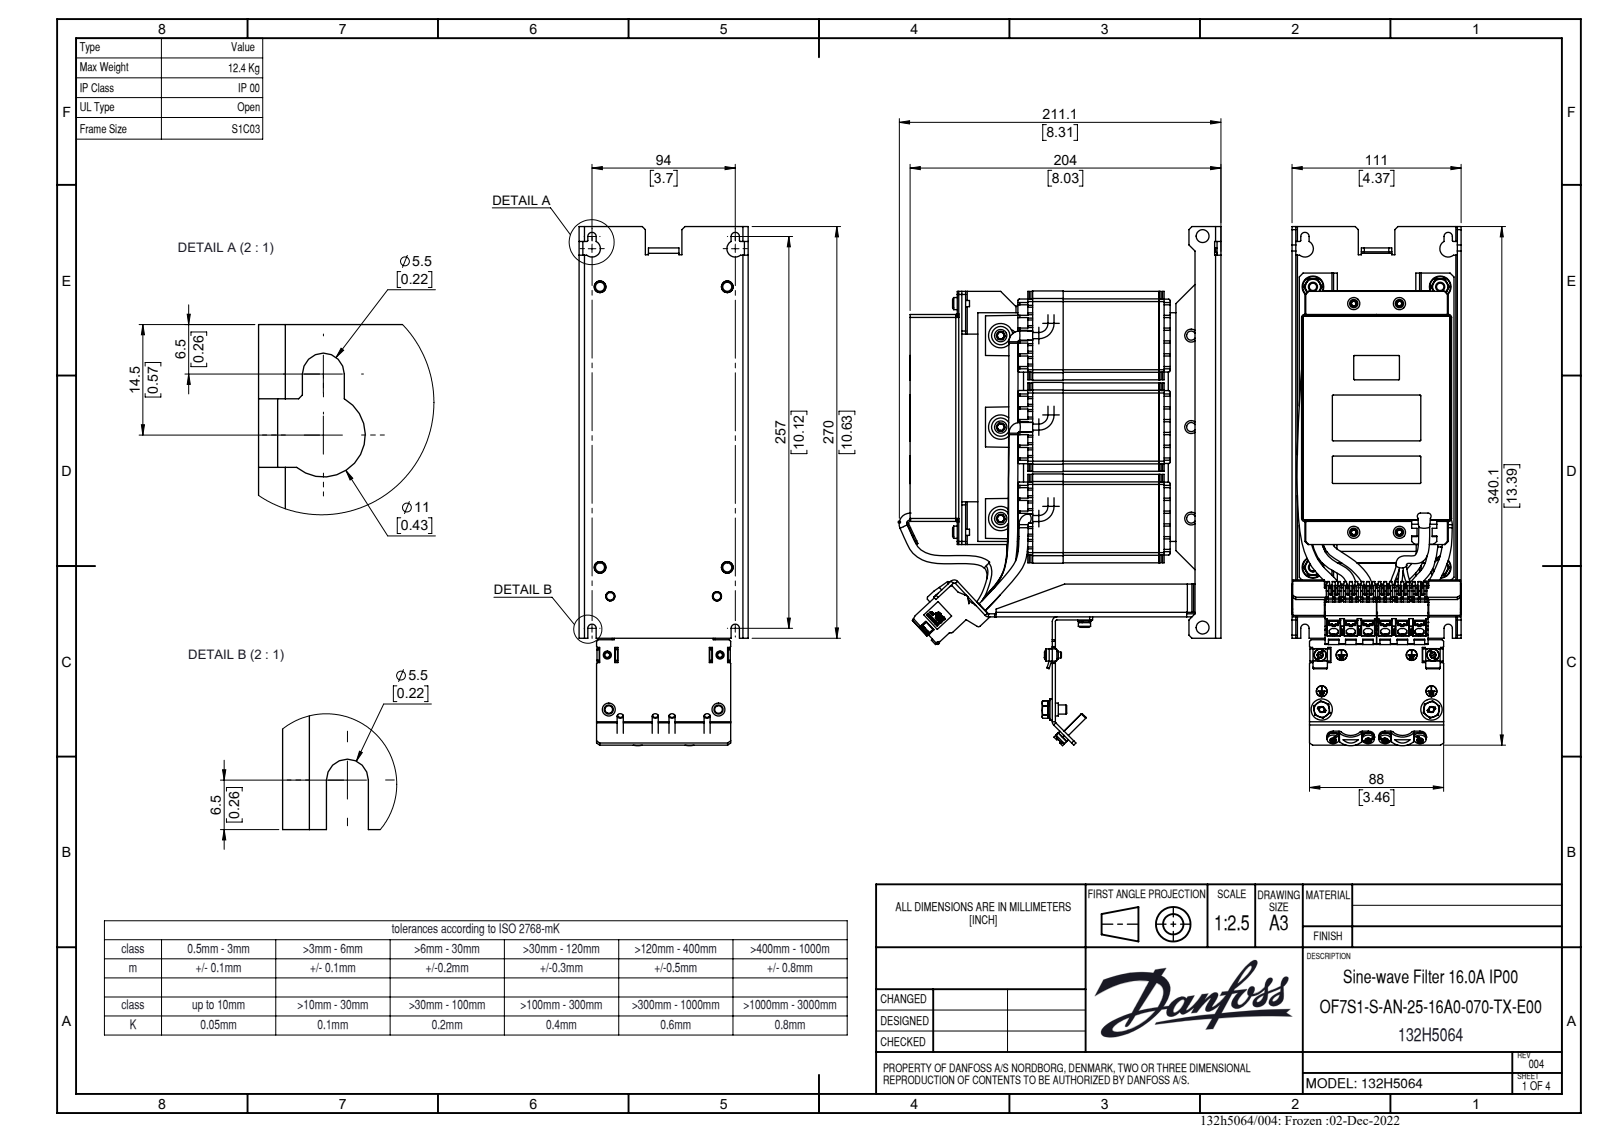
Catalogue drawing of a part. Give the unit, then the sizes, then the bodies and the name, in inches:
Units: inches
Overall size (bounding box): 13.406 × 8.11 × 4.37
Round holes (diameter × count): ⌀0.156 ×5, ⌀0.157 ×4, ⌀0.22 ×4, ⌀0.236 ×4, ⌀0.252 ×4, ⌀0.13 ×3, ⌀0.172 ×2, ⌀0.177 ×2, ⌀0.197 ×2, ⌀0.224 ×2, ⌀0.335 ×2, ⌀0.165 ×1
Round bosses / shafts (diameter × count): ⌀0.315 ×12, ⌀0.236 ×7, ⌀0.472 ×6, ⌀0.335 ×5, ⌀0.157 ×4, ⌀0.63 ×3, ⌀0.551 ×2, ⌀0.331 ×1
Partial cylindrical surfaces — rounded edges, fillets, slot ends (radius × count): R0.039 ×6, R0.108 ×4, R0.138 ×3, R0.118 ×2, R0.217 ×2, R0.295 ×2, R0.354 ×2, R0.079 ×1
Main face-to-face distances: 0.079, 0.098, 2.362, 2.283, 1.291, 4.811, 1.073, 6.594, 1.181, 0.11
Hole centre spacings: 2.362, 5.459, 4.921, 0.794, 1.139, 1.181, 1.389, 1.408
Volume: 156.3 in³ · Surface area: 623.7 in²
Bodies: 13 solids, 1437 faces (1239 planar, 198 cylindrical, 0 other)
Part name (STEP PRODUCT): 132H5064-V001-030222
STEP written by: CREO PARAMETRIC BY PTC INC, 2020342 (CONFIG_CONTROL_DESIGN)
